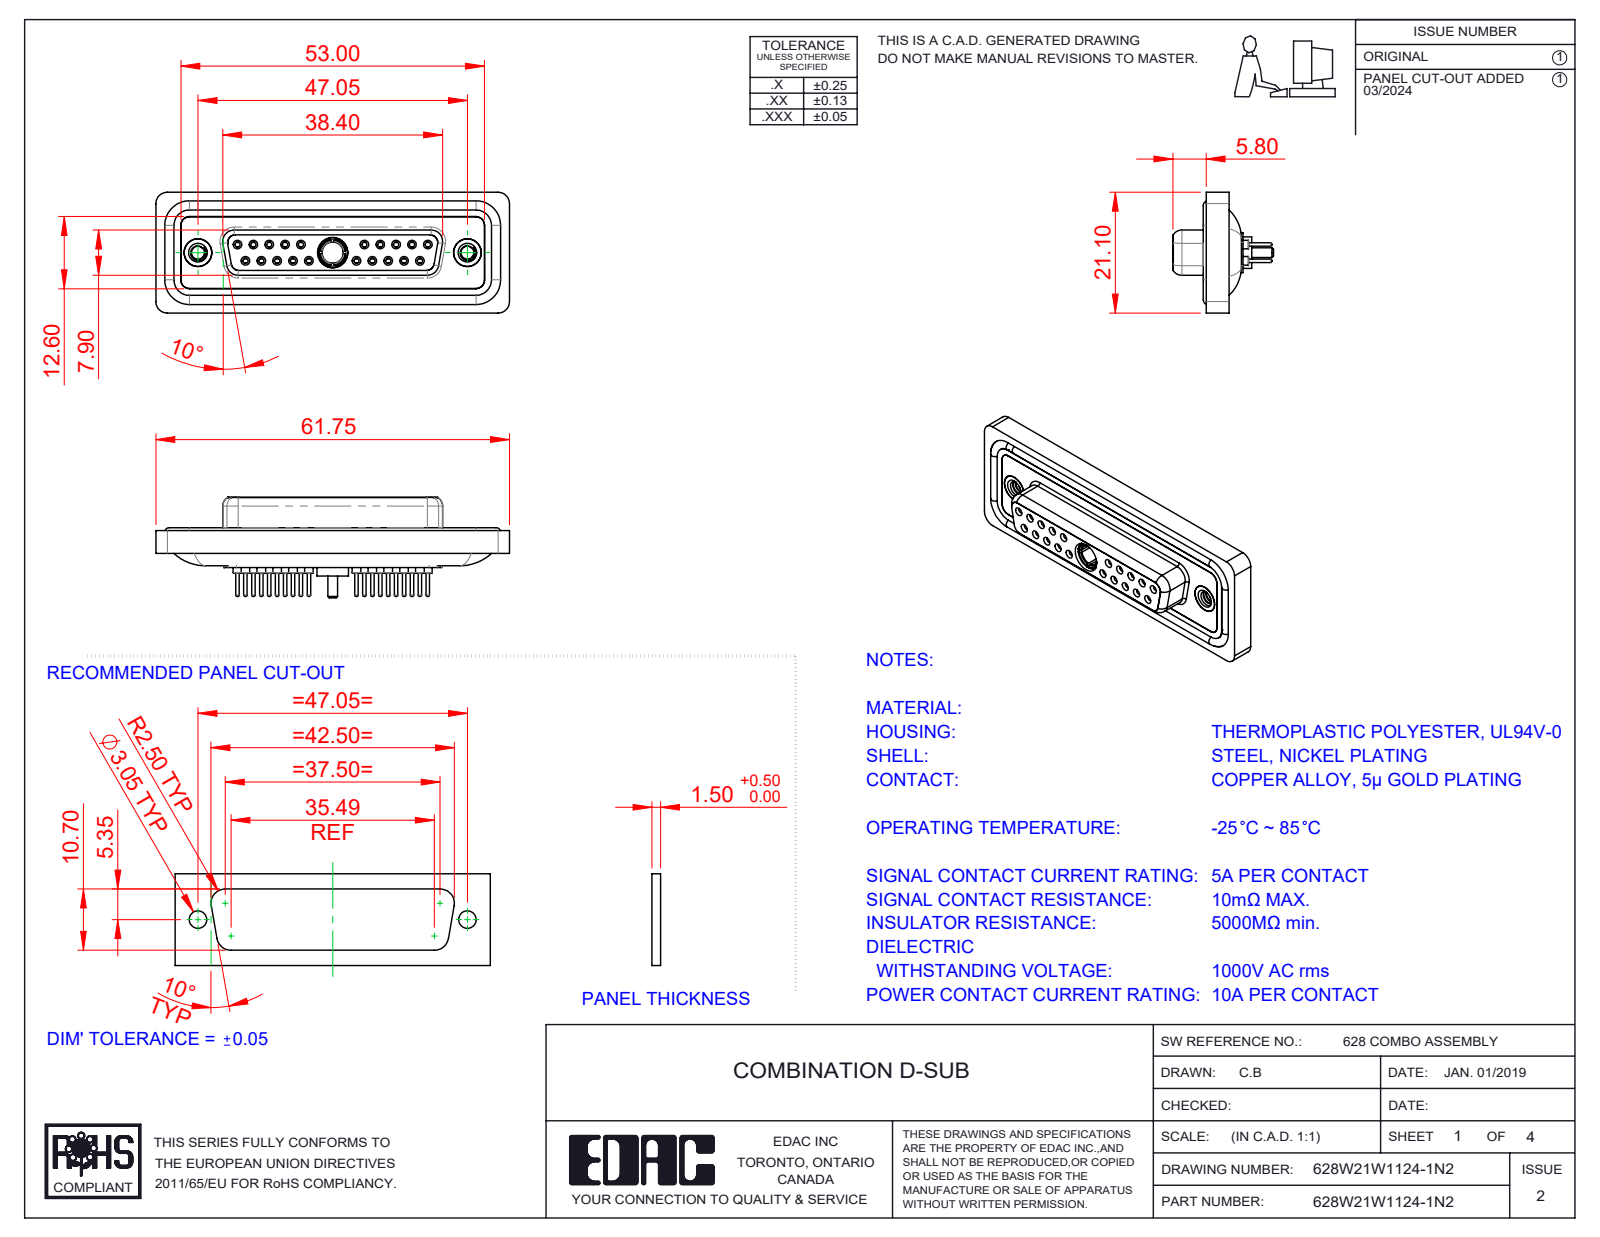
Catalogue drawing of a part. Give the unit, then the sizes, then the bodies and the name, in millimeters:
Units: millimetres
Overall size (bounding box): 61.75 × 21.1 × 17.55
Round holes (diameter × count): ⌀0.9 ×20, ⌀1.1 ×20, ⌀1.5 ×20, ⌀2 ×20, ⌀1.6 ×10, ⌀1.7 ×10, ⌀4.85 ×3, ⌀2.26 ×2, ⌀4 ×2, ⌀4.05 ×2, ⌀5 ×2, ⌀3.7 ×1
Round bosses / shafts (diameter × count): ⌀2.2 ×20, ⌀0.6 ×20, ⌀1.6 ×14, ⌀4.95 ×2, ⌀4.8 ×2, ⌀5.5 ×1, ⌀5.2 ×1, ⌀4.96 ×1
Partial cylindrical surfaces — rounded edges, fillets, slot ends (radius × count): R1.5 ×22, R2 ×18, R1.35 ×8, R1.6 ×8, R0.25 ×4, R0.5 ×4, R0.6 ×4, R0.65 ×4
Main face-to-face distances: 0.4, 1.8, 7.45, 6.6, 5.65, 0.5, 1.6, 7.05, 2.9, 1.1
Hole centre spacings: 3.16, 2.77, 5.54, 5.03, 8.31, 7.48, 16.62, 19.39
Volume: 8 359 mm³ · Surface area: 13 989 mm²
Bodies: 29 solids, 1560 faces (434 planar, 591 cylindrical, 535 other)
Part name (STEP PRODUCT): 628Combo Threaded Rivet_2; Power Socket_10A S; 628Combo Shell Rear_25 Contacts; 628Combo Shell Front_25 Contacts (+5 more)
STEP written by: SolidWorks 2023 (CONFIG_CONTROL_DESIGN)
